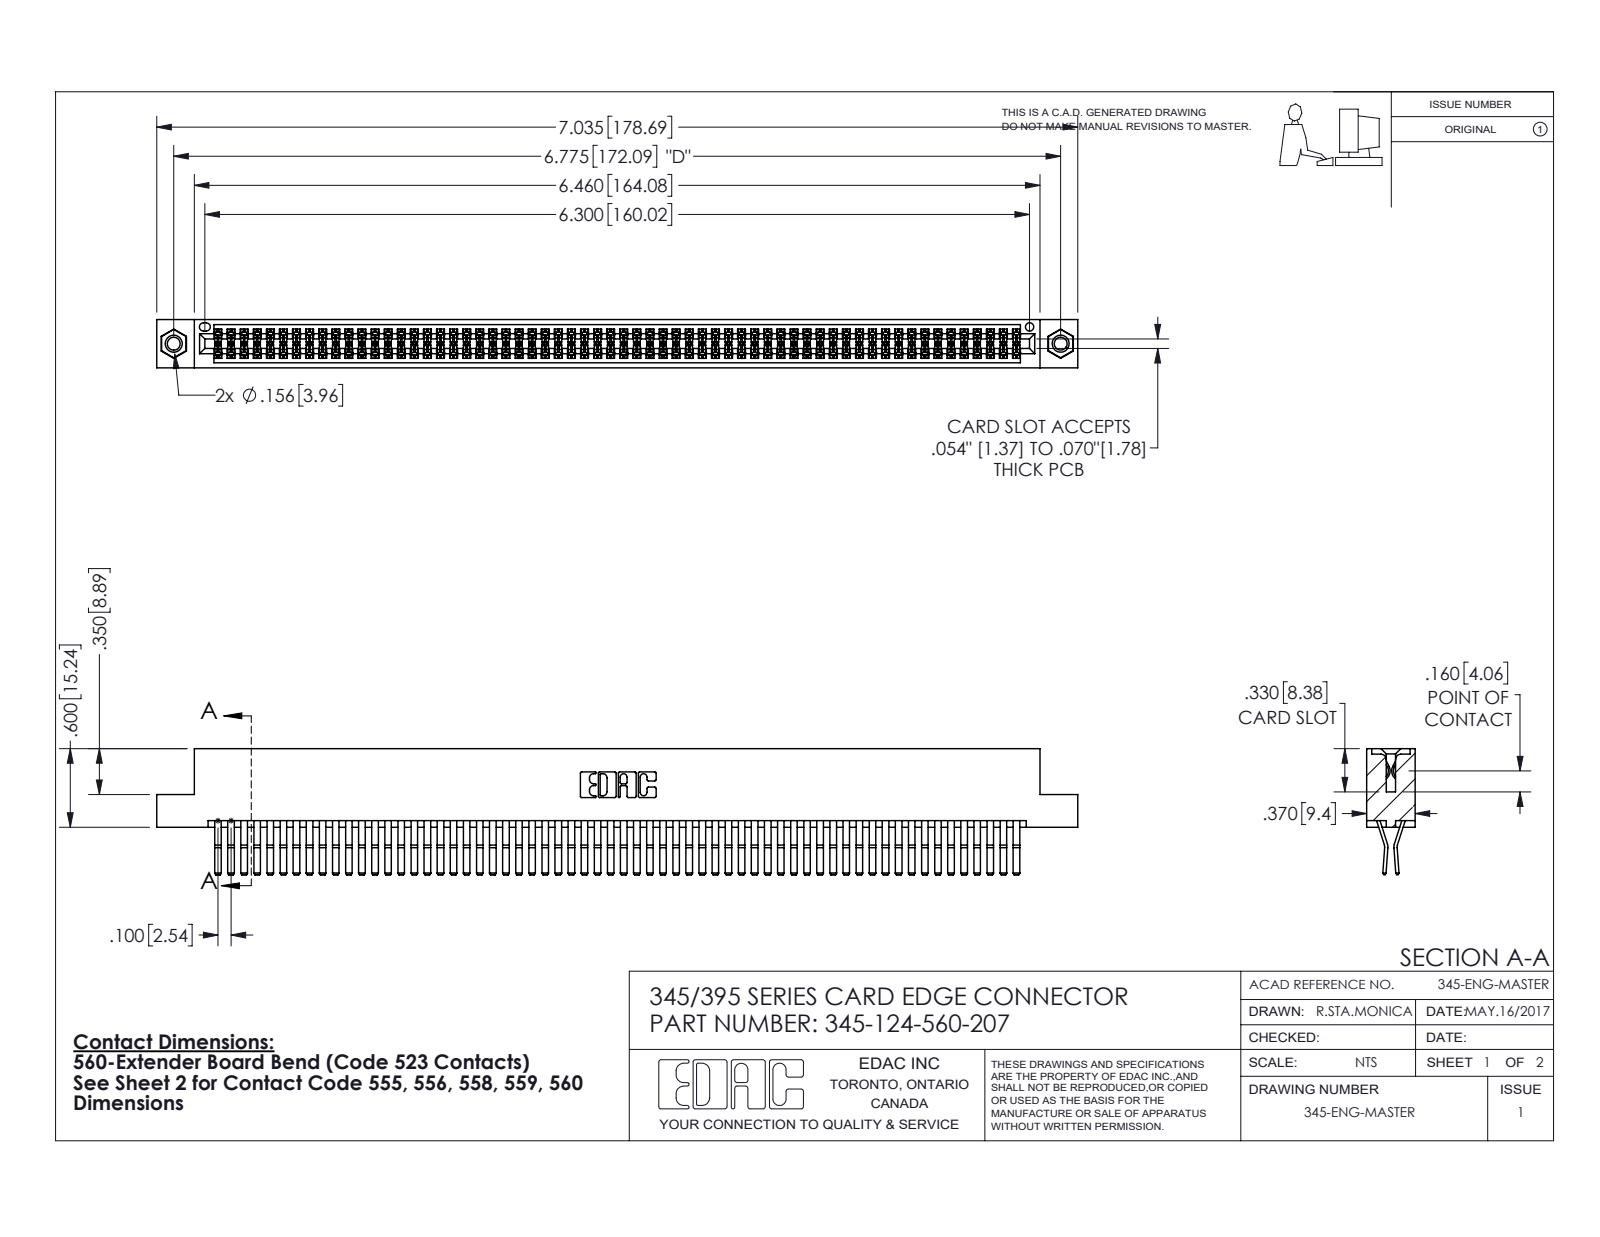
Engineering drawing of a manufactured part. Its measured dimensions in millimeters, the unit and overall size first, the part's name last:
Units: millimetres
Overall size (bounding box): 178.7 × 24.4 × 9.4
Round holes (diameter × count): ⌀2.5 ×2, ⌀3.2 ×2, ⌀4 ×2, ⌀1.6 ×1
Round bosses / shafts (diameter × count): ⌀3.9 ×2
Partial cylindrical surfaces — rounded edges, fillets, slot ends (radius × count): R0.2 ×186, R0.3 ×22, R0.2 ×6, R0.8 ×6, R0.7 ×3, R0.3 ×2, R0.4 ×2, R0.5 ×2
Main face-to-face distances: 0.6, 1.8, 7.6, 9.4, 5.1, 2.5, 6.9, 5.7, 4.4, 3.8
Hole centre spacings: 6.9, 166.1, 172.1
Volume: 18 340 mm³ · Surface area: 29 620 mm²
Bodies: 127 solids, 6634 faces (4204 planar, 2414 cylindrical, 16 other)
Part name (STEP PRODUCT): 345-124-560-207; 345-250-001_345-250-005-103; 345-292-001_560 Tail; 345 Part_Flush Mounting Lugs - 0.156 Dia-TI
STEP written by: SolidWorks 2016 (CONFIG_CONTROL_DESIGN)
